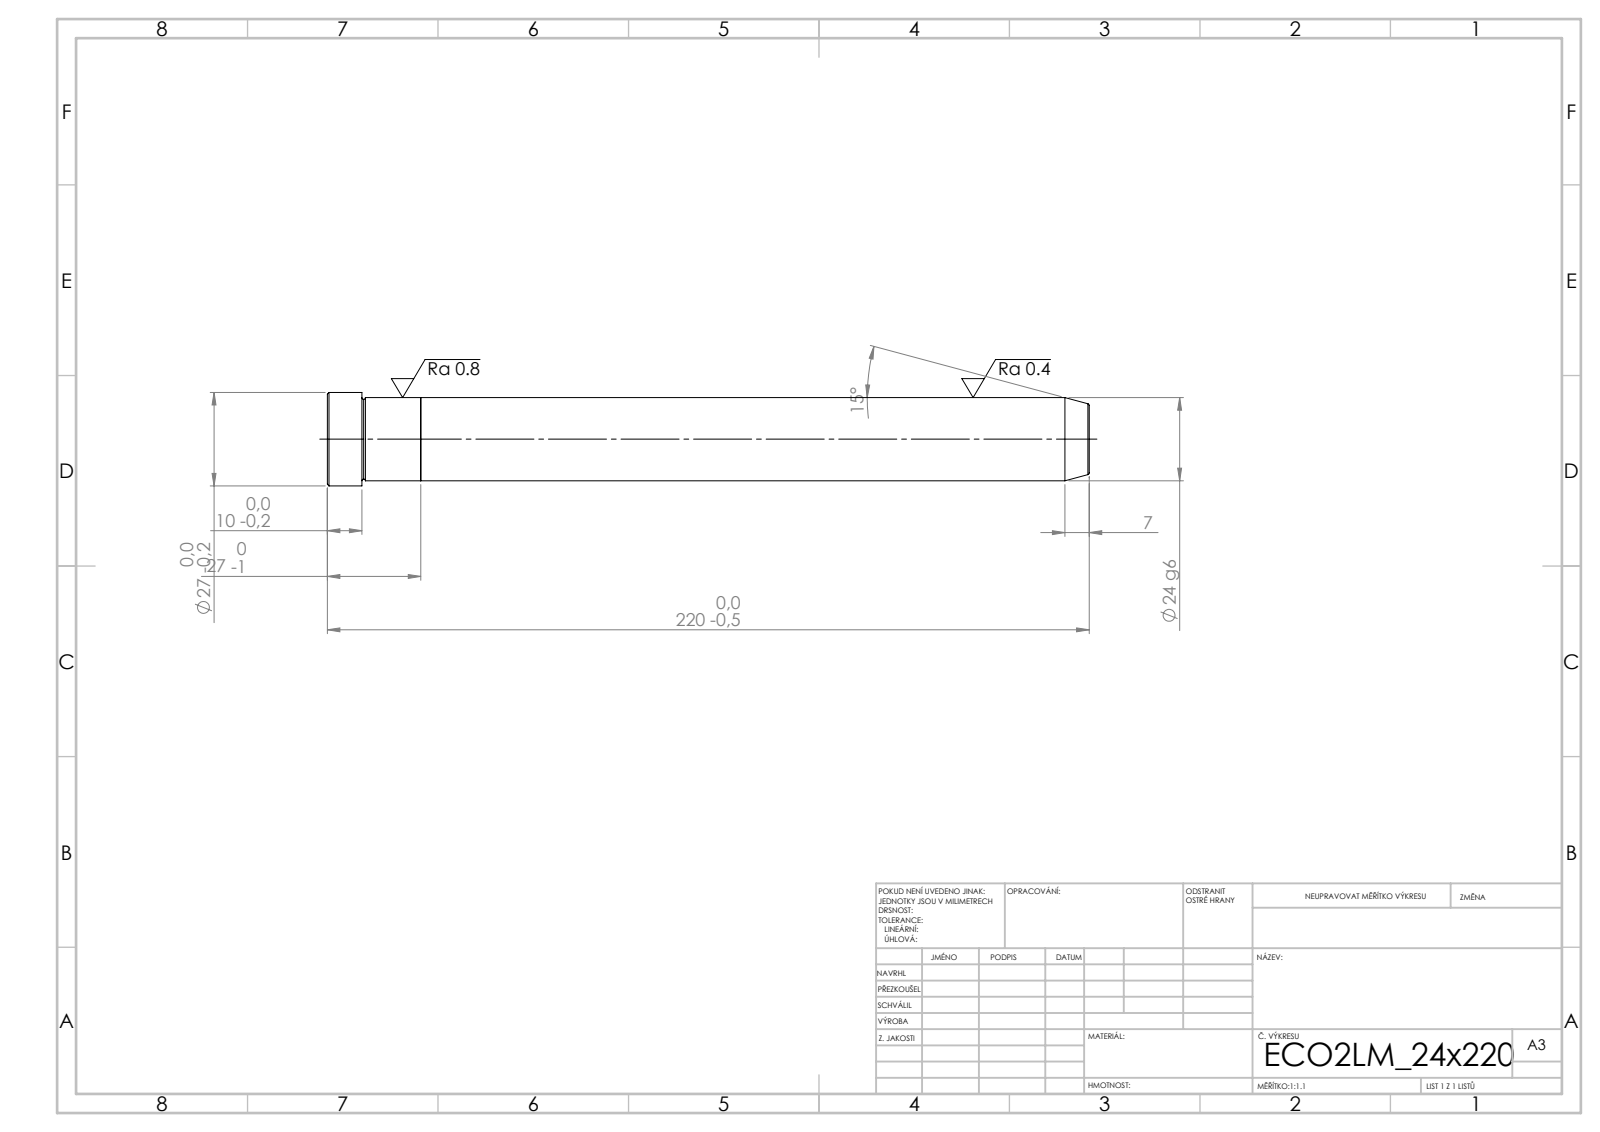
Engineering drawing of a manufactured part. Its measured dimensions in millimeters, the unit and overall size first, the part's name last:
Units: millimetres
Overall size (bounding box): 220 × 27 × 27
Round bosses / shafts (diameter × count): ⌀27 ×1, ⌀24 ×1
Main face-to-face distances: 27, 193, 220, 210, 17, 10
Volume: 100 217 mm³ · Surface area: 18 585 mm²
Bodies: 2 solids, 21 faces (5 planar, 6 cylindrical, 10 other)
STEP written by: SolidWorks 2019 (CONFIG_CONTROL_DESIGN)
